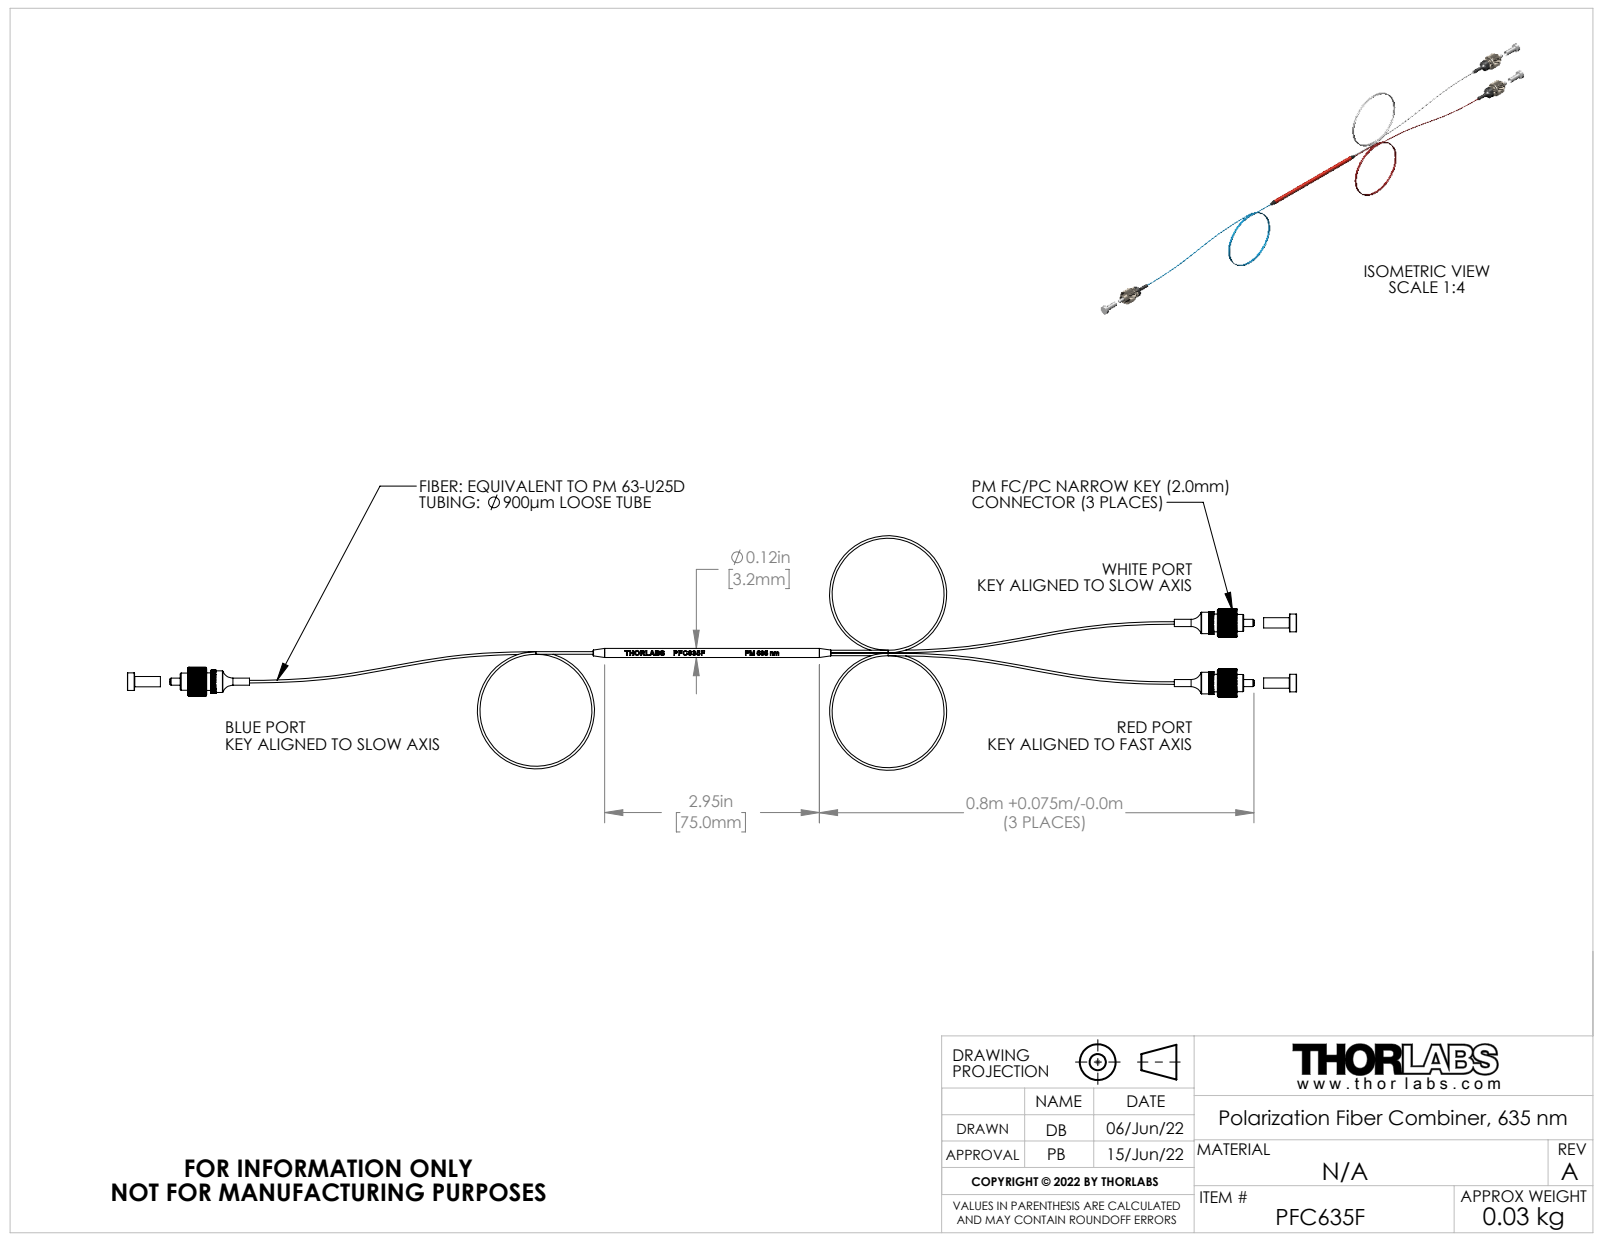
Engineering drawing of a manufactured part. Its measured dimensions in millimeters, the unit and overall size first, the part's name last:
Units: millimetres
Overall size (bounding box): 408.3 × 81.9 × 13.99
Round holes (diameter × count): ⌀0.5 ×6, ⌀1 ×5, ⌀0.9 ×3, ⌀2.5 ×3, ⌀2.8 ×3, ⌀3.36 ×3, ⌀4.38 ×3, ⌀4.4 ×3, ⌀5.08 ×3, ⌀5.55 ×3, ⌀6.1 ×3, ⌀6.5 ×3
Round bosses / shafts (diameter × count): ⌀7.5 ×3, ⌀7.07 ×3, ⌀6.17 ×3, ⌀6.08 ×3, ⌀5.95 ×3, ⌀5.38 ×3, ⌀4.85 ×3, ⌀3.6 ×3
Partial cylindrical surfaces — rounded edges, fillets, slot ends (radius × count): R0.5 ×6, R0.75 ×3, R1.55 ×3, R2.26 ×3, R3.98 ×3, R5 ×3, R0.45 ×2, R1 ×1
Main face-to-face distances: 6.86, 6.85, 2, 1.43, 4.97, 349.97, 1.54, 2.97, 3.43, 27.68
Hole centre spacings: 10.2, 10.69, 0.5, 11.18, 1, 4.03, 9.71, 20.5
Volume: 3 272 mm³ · Surface area: 13 572 mm²
Bodies: 32 solids, 2605 faces (1271 planar, 882 cylindrical, 452 other)
Part name (STEP PRODUCT): TTN174105-E0W; DWG1553; PANDA 635_60; SGP-418011K0G (+8 more)
STEP written by: SolidWorks 2020 (CONFIG_CONTROL_DESIGN)
